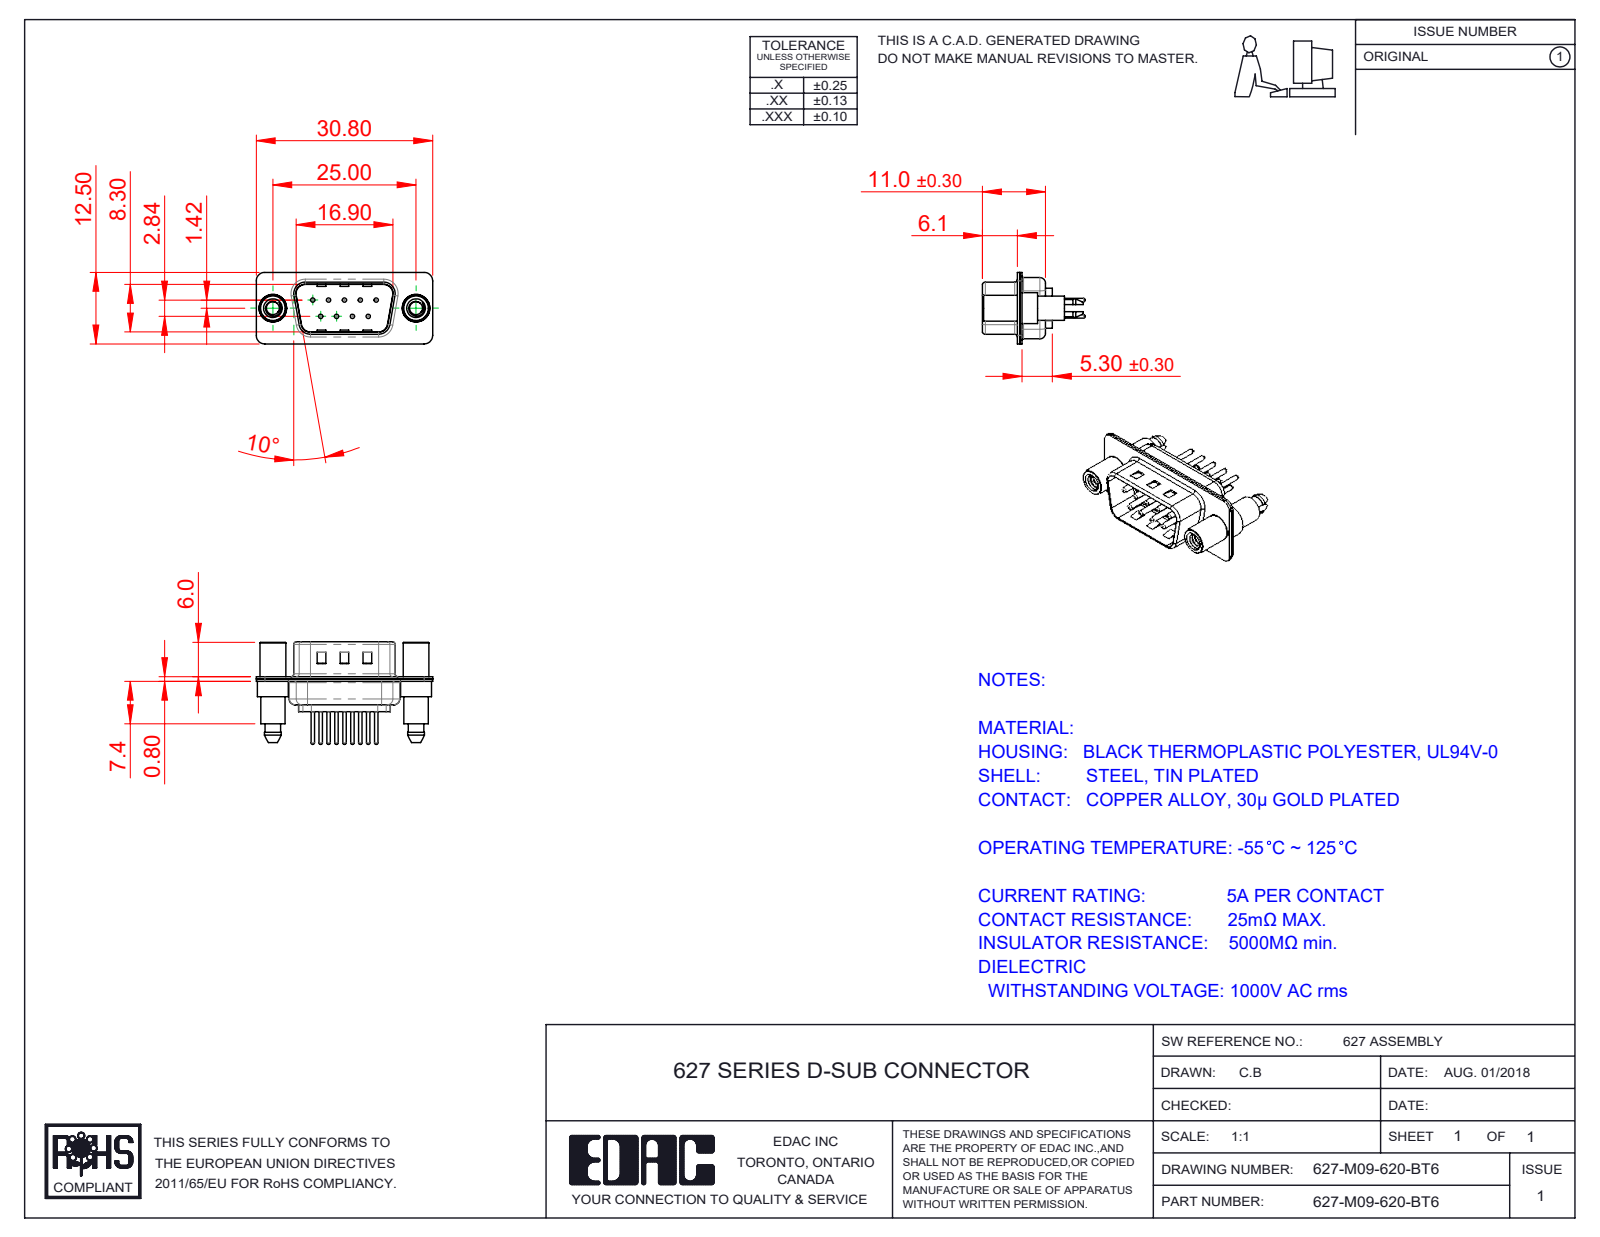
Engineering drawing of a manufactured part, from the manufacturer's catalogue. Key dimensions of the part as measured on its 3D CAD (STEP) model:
Part name (STEP PRODUCT): 627M Shell Rear_09 Contacts; 627M Shell Front_09 Contacts; 627-M09-620-BT6; 627M Contact Row 1_20 (+3 more)
STEP written by: SolidWorks 2020 (CONFIG_CONTROL_DESIGN)
Units: millimetres
Bodies: 14 solids, 689 faces (188 planar, 283 cylindrical, 218 other)
Overall size (bounding box): 30.8 × 17.9 × 12.5
Volume: 1 649 mm³ · Surface area: 4 042 mm²
Round holes (diameter × count): ⌀0.75 ×9, ⌀1.6 ×9, ⌀2 ×9, ⌀2.26 ×2, ⌀4 ×2, ⌀4.8 ×2
Round bosses / shafts (diameter × count): ⌀1.5 ×9, ⌀0.6 ×9, ⌀5.4 ×2, ⌀4.9 ×2, ⌀4.5 ×2, ⌀4.25 ×2
Partial cylindrical surfaces — rounded edges, fillets, slot ends (radius × count): R1.5 ×18, R2 ×12, R1.6 ×10, R0.5 ×8, R0.25 ×4, R0.6 ×4, R0.65 ×4, R0.9 ×4
Main face-to-face distances: 0.4, 0.8, 9.5, 9.1, 8.7, 0.65, 9.9, 1.2, 5.3, 6.1
Hole centre spacings: 3.16, 2.77, 5.54, 5.03, 5.04, 8.31, 7.1, 7.48
